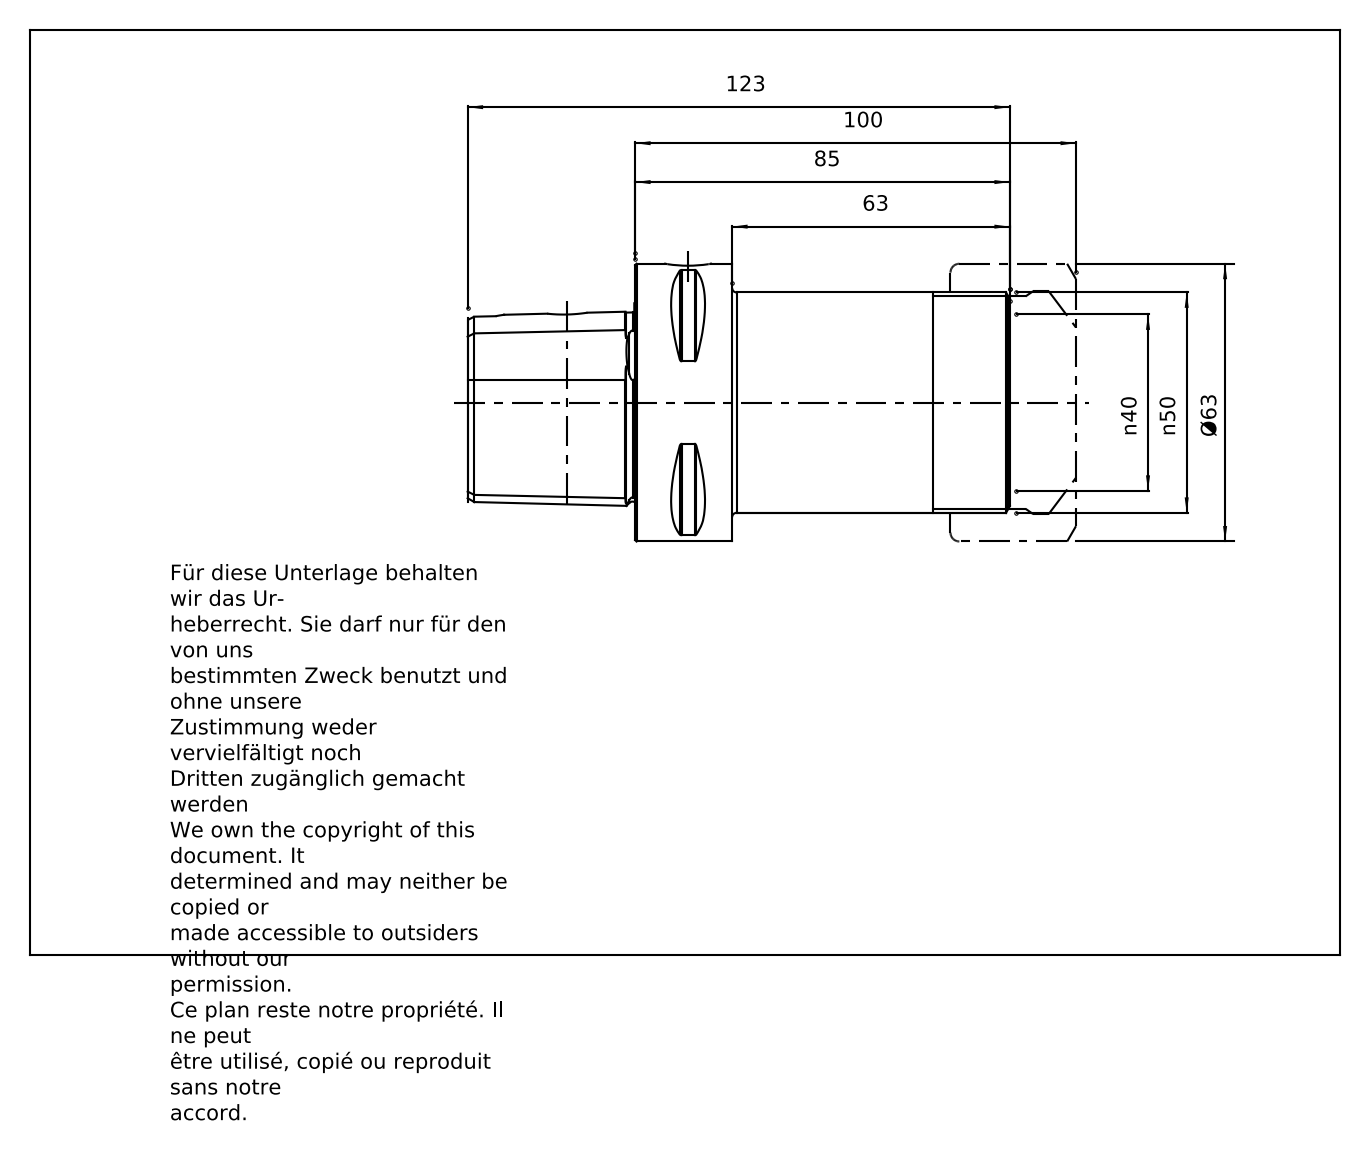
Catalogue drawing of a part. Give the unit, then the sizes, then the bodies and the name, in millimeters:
Units: millimetres
Overall size (bounding box): 138 × 63 × 63
Round holes (diameter × count): ⌀4.25 ×1, ⌀8.1 ×1, ⌀10.04 ×1, ⌀18 ×1, ⌀28.02 ×1, ⌀30.5 ×1, ⌀32 ×1
Round bosses / shafts (diameter × count): ⌀63 ×1, ⌀50 ×1, ⌀20 ×1
Partial cylindrical surfaces — rounded edges, fillets, slot ends (radius × count): R0.5 ×8, R2.7 ×6, R6 ×1
Main face-to-face distances: 25.5, 74.5, 100, 38, 85, 22, 52.5, 78, 47, 25
Hole centre spacings: 27.5
Volume: 258 722 mm³ · Surface area: 45 836 mm²
Bodies: 2 solids, 164 faces (51 planar, 41 cylindrical, 72 other)
Part name (STEP PRODUCT): CC6-021-40; 83-912-40; CC6-021-40_ASM
STEP written by: PRO/ENGINEER BY PARAMETRIC TECHNOLOGY CORPORATION, 2010430 (CONFIG_CONTROL_DESIGN)
